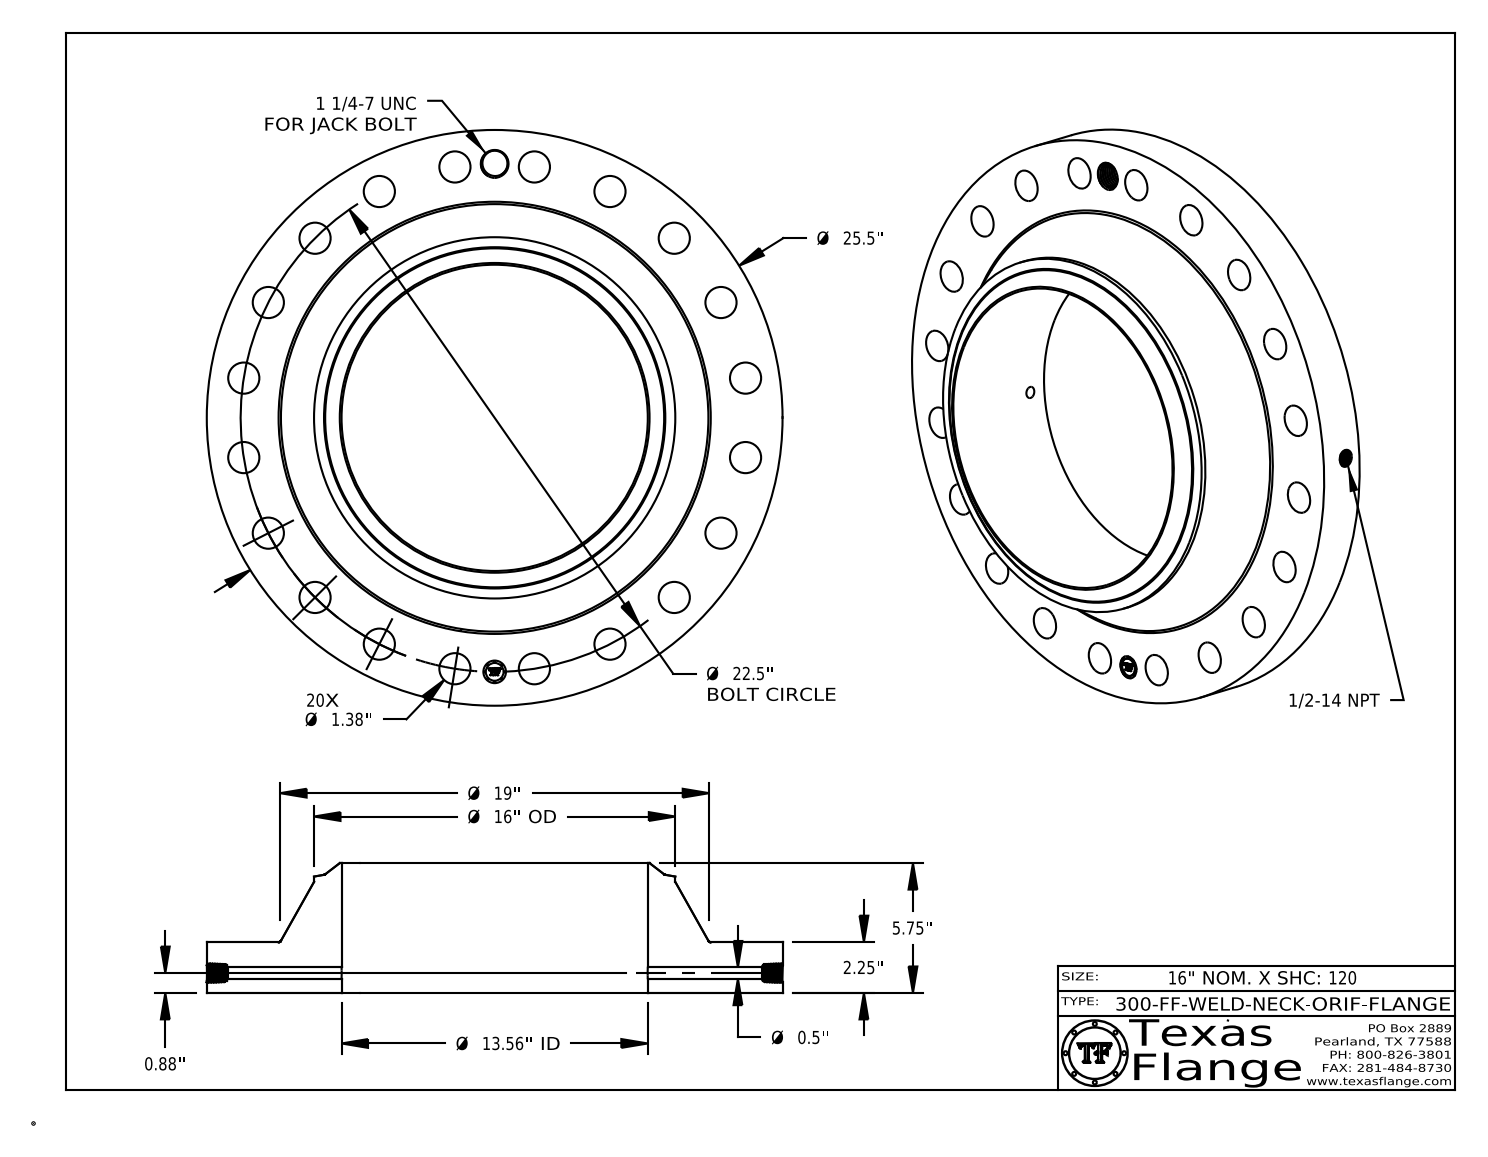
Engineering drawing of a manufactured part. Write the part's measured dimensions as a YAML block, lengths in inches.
part_name: "300-FF-WELD-NECK"
step_written_by: "CATIA V5 STEP AP214 (AUTOMOTIVE_DESIGN)"
units: inches
bodies: {solids: 1, faces: 800, planar: 368, cylindrical: 117, other: 315}
overall_size: [25.5, 25.5, 5.75]
volume: 1036
surface_area: 1430
round_holes:
  - {diameter: 1.38, count: 20}
  - {diameter: 0.5, count: 1}
  - {diameter: 0.672, count: 1}
  - {diameter: 1, count: 1}
  - {diameter: 1.109, count: 1}
  - {diameter: 13.562, count: 1}
round_bosses_or_shafts:
  - {diameter: 0.061, count: 8}
  - {diameter: 25.5, count: 1}
  - {diameter: 16, count: 1}
  - {diameter: 0.788, count: 1}
face_to_face_distances: [2.25, 5.75, 3.5, 2.235, 0.015, 3.515, 0.298, 0.293, 0.054, 0.248]
hole_center_spacings: [3.52, 10.215, 18.203, 20.048, 21.399, 6.953, 11.25, 13.225]
